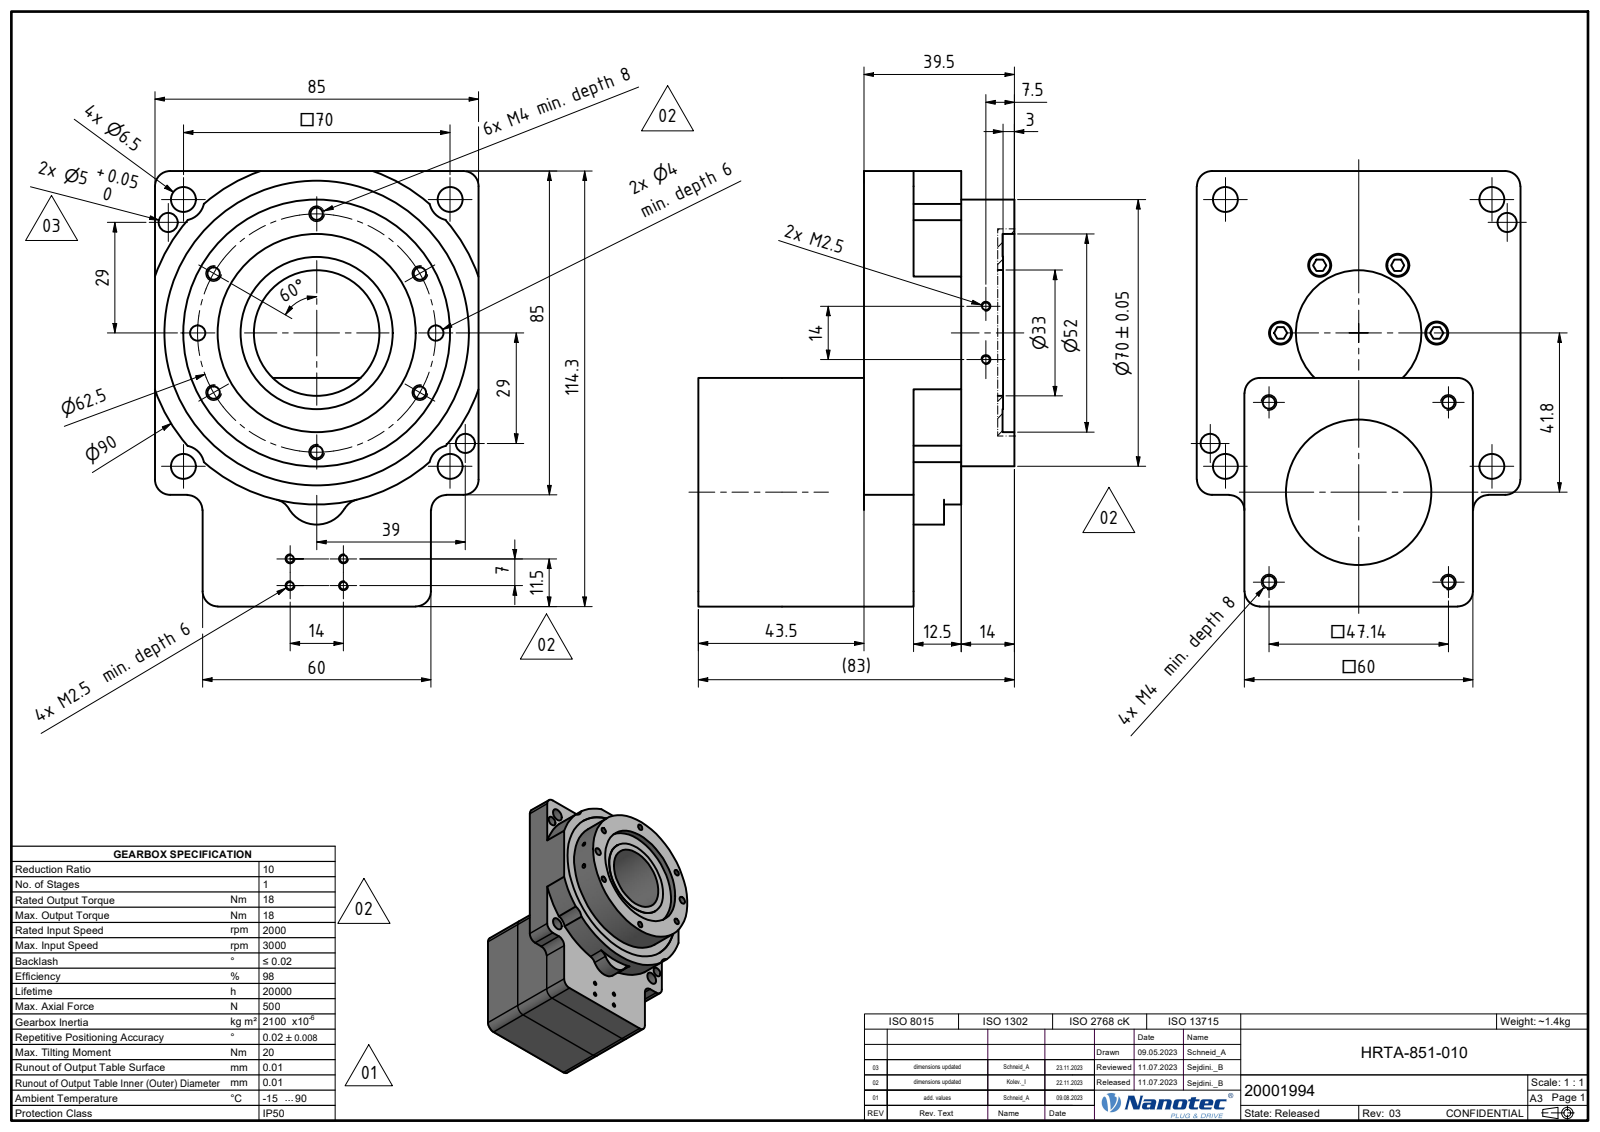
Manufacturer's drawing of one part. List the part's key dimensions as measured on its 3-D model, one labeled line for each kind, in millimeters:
Part name (STEP PRODUCT): 上海固佐 ZTN085-10(6.35-38.1-47.14-47.14)
STEP written by: Autodesk Inventor 2021 (AUTOMOTIVE_DESIGN)
Units: millimetres
Bodies: 1 solid, 283 faces (167 planar, 100 cylindrical, 16 other)
Overall size (bounding box): 114.3 × 85 × 83
Volume: 349 787 mm³ · Surface area: 56 417 mm²
Round holes (diameter × count): ⌀3.3 ×10, ⌀2.05 ×6, ⌀3.5 ×6, ⌀6 ×6, ⌀6.5 ×4, ⌀8 ×4, ⌀4 ×2, ⌀5 ×2, ⌀8.1 ×2, ⌀30 ×1, ⌀33 ×1, ⌀38.1 ×1
Round bosses / shafts (diameter × count): ⌀5.5 ×6, ⌀7 ×4, ⌀8 ×2, ⌀70 ×1, ⌀49.9 ×1, ⌀40 ×1, ⌀39 ×1
Partial cylindrical surfaces — rounded edges, fillets, slot ends (radius × count): R4 ×12, R2 ×8, R5.5 ×4, R12 ×1, R25 ×1, R45 ×1
Main face-to-face distances: 60, 12.5, 72.5, 13, 56.5, 43.5, 39.5, 26.5, 83, 85
Hole centre spacings: 31.25, 35.2, 74.93, 20.5, 27.5, 10.75, 31.24, 33.33
